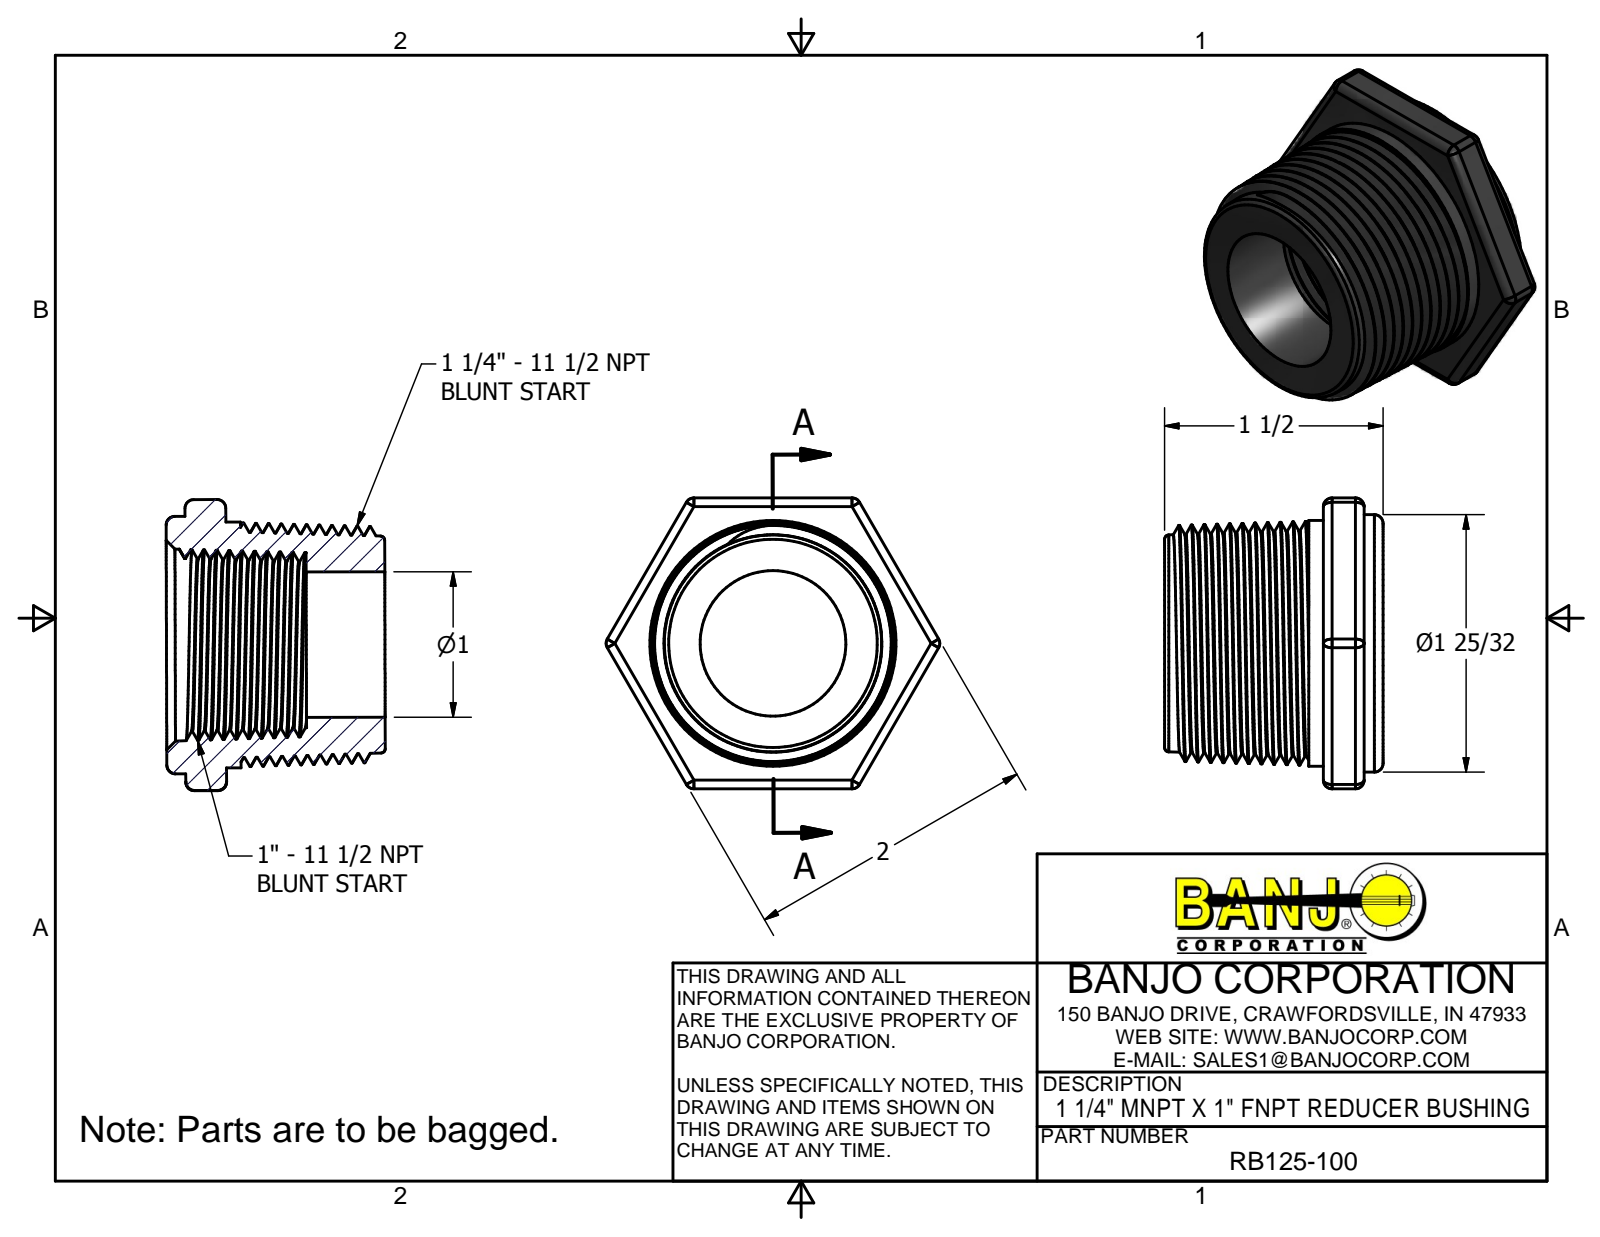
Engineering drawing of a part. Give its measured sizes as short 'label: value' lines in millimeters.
name: RB125-100
written by: Autodesk Inventor 2014 (AUTOMOTIVE_DESIGN)
unit: mm
bodies: 1 solid, 82 faces (12 planar, 23 cylindrical, 47 other)
size: 58.19 × 50.8 × 38.1
volume: 30 104 mm³; area: 15 521 mm²
holes: 1× ⌀25.4
bosses: 1× ⌀44.96, 1× ⌀42.93
rounds: 18× R1.52, 1× R10, 1× R11.11
face distances: 27.69, 7.11, 34.8, 50.8, 3.3, 10.41, 38.1, 24.38, 21.08, 13.97
